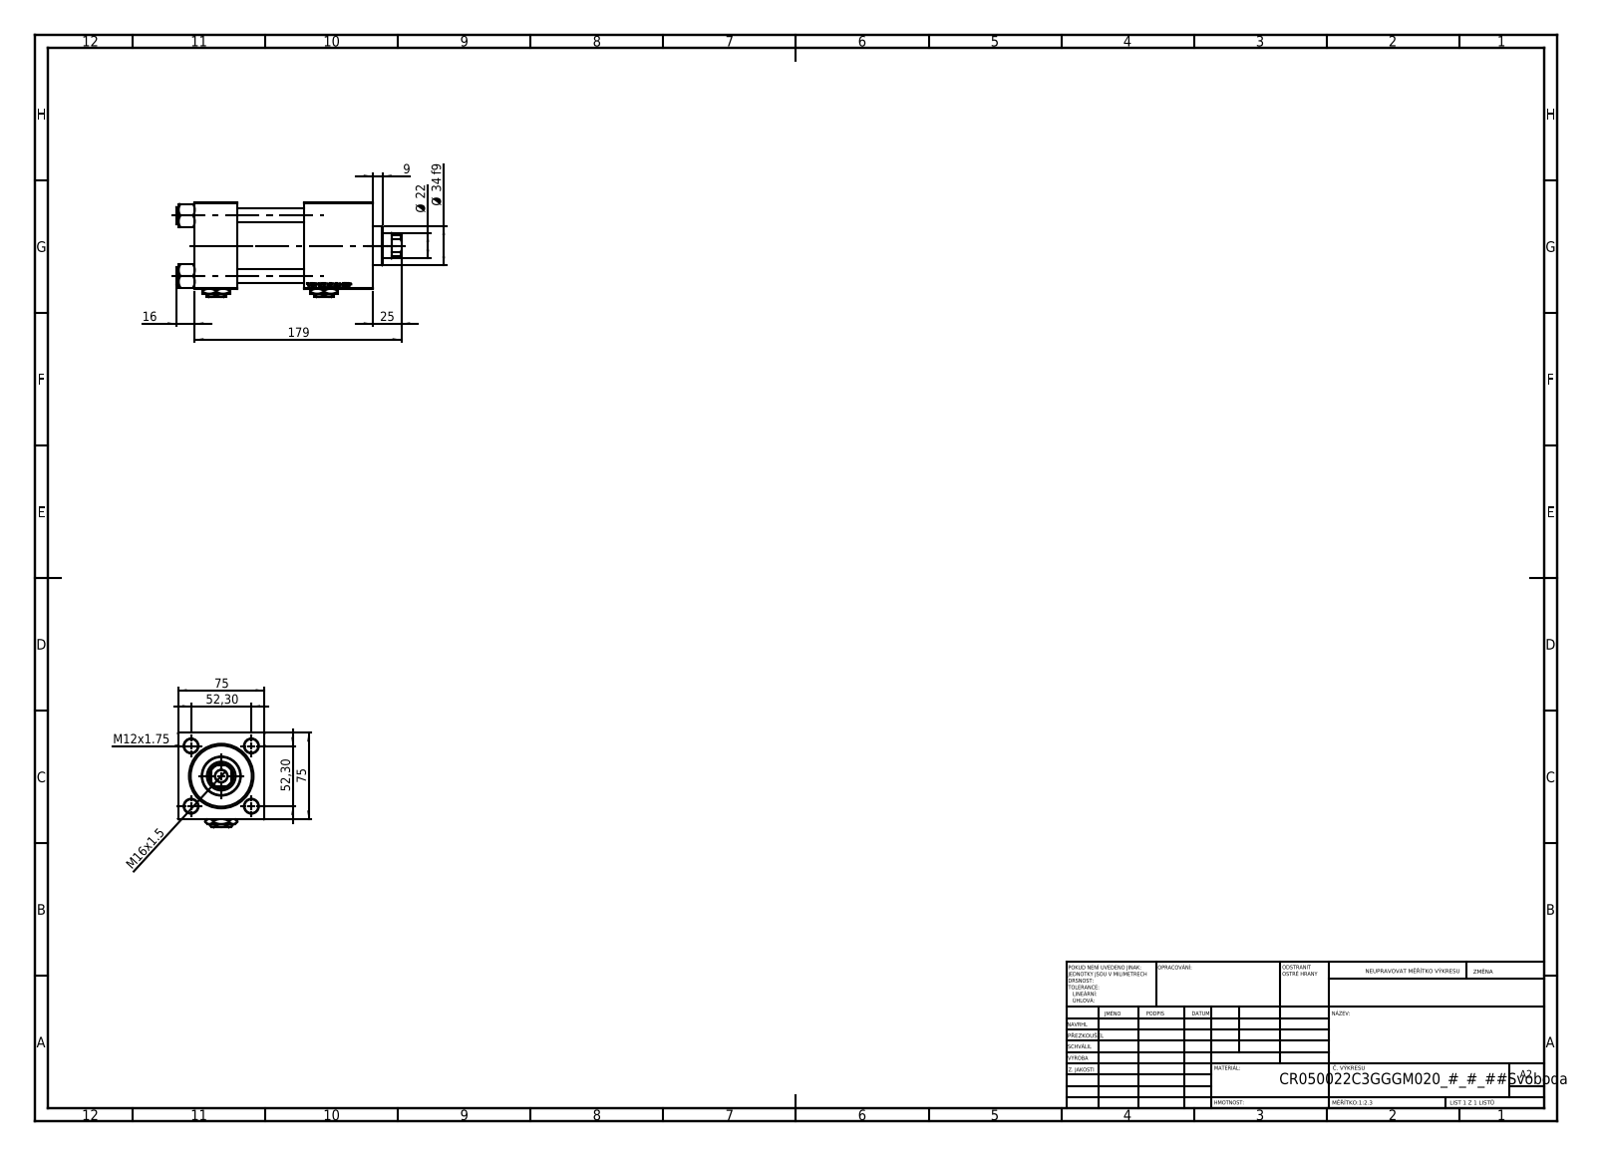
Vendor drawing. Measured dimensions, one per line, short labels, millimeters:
name: V215CR_C_TYCINKA; V215CR_C_Body; NUT_M5_C; V215_VC_A (+2 more)
written by: SolidWorks 2019 (CONFIG_CONTROL_DESIGN)
unit: mm
bodies: 13 solids, 1249 faces (573 planar, 98 cylindrical, 578 other)
size: 195 × 82 × 75.54
volume: 651 251 mm³; area: 151 878 mm²
holes: 4× ⌀12, 2× ⌀7, 2× ⌀20.96, 2× ⌀30, 1× ⌀10.5, 1× ⌀22, 1× ⌀25, 1× ⌀41, 1× ⌀50, 1× ⌀53
bosses: 4× ⌀15, 1× ⌀56, 1× ⌀34
rounds: 1× R10.5
face distances: 75, 37, 154, 117, 95, 59, 58, 125.3, 88.3, 30.3
hole spacings: 36.98, 52.3, 73.96, 93.5
